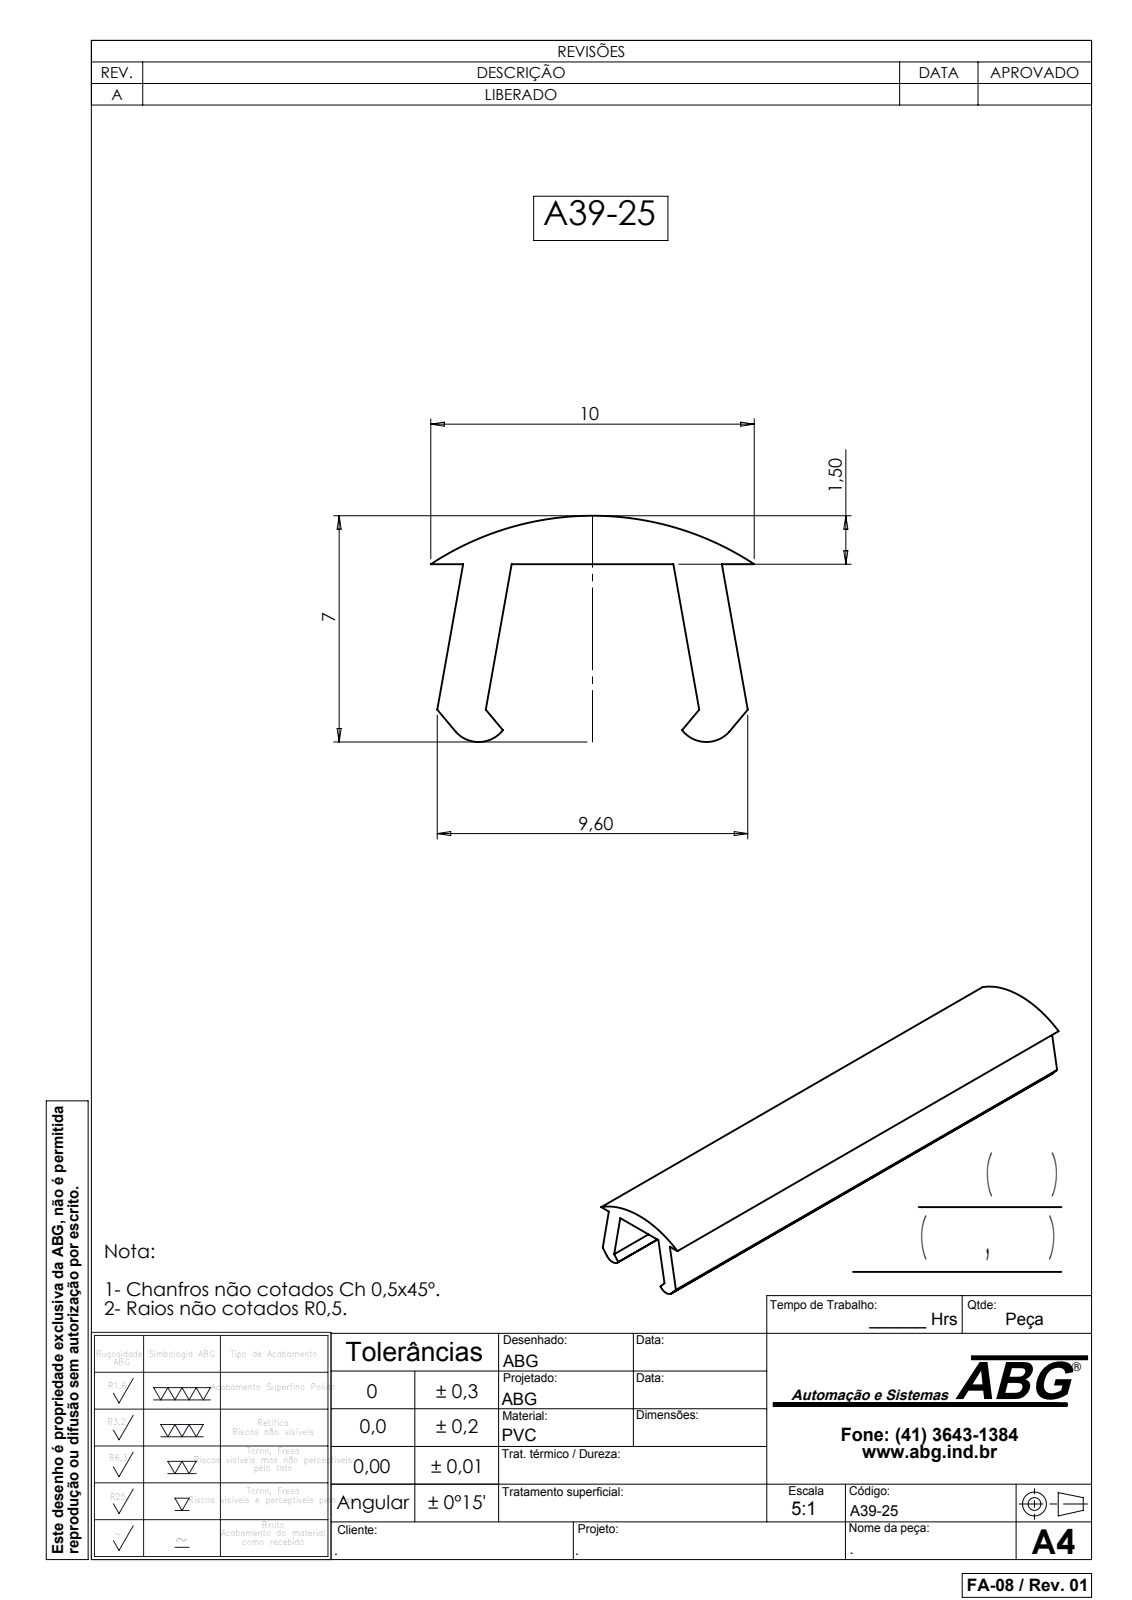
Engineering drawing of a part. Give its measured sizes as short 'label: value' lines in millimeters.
name: A39-25
written by: SolidWorks 2007 (CONFIG_CONTROL_DESIGN)
unit: mm
bodies: 1 solid, 16 faces (13 planar, 3 cylindrical, 0 other)
size: 50 × 10 × 7
volume: 1 317 mm³; area: 2 184 mm²
rounds: 2× R0.95, 1× R9.08
face distances: 1.48, 1.15, 50
